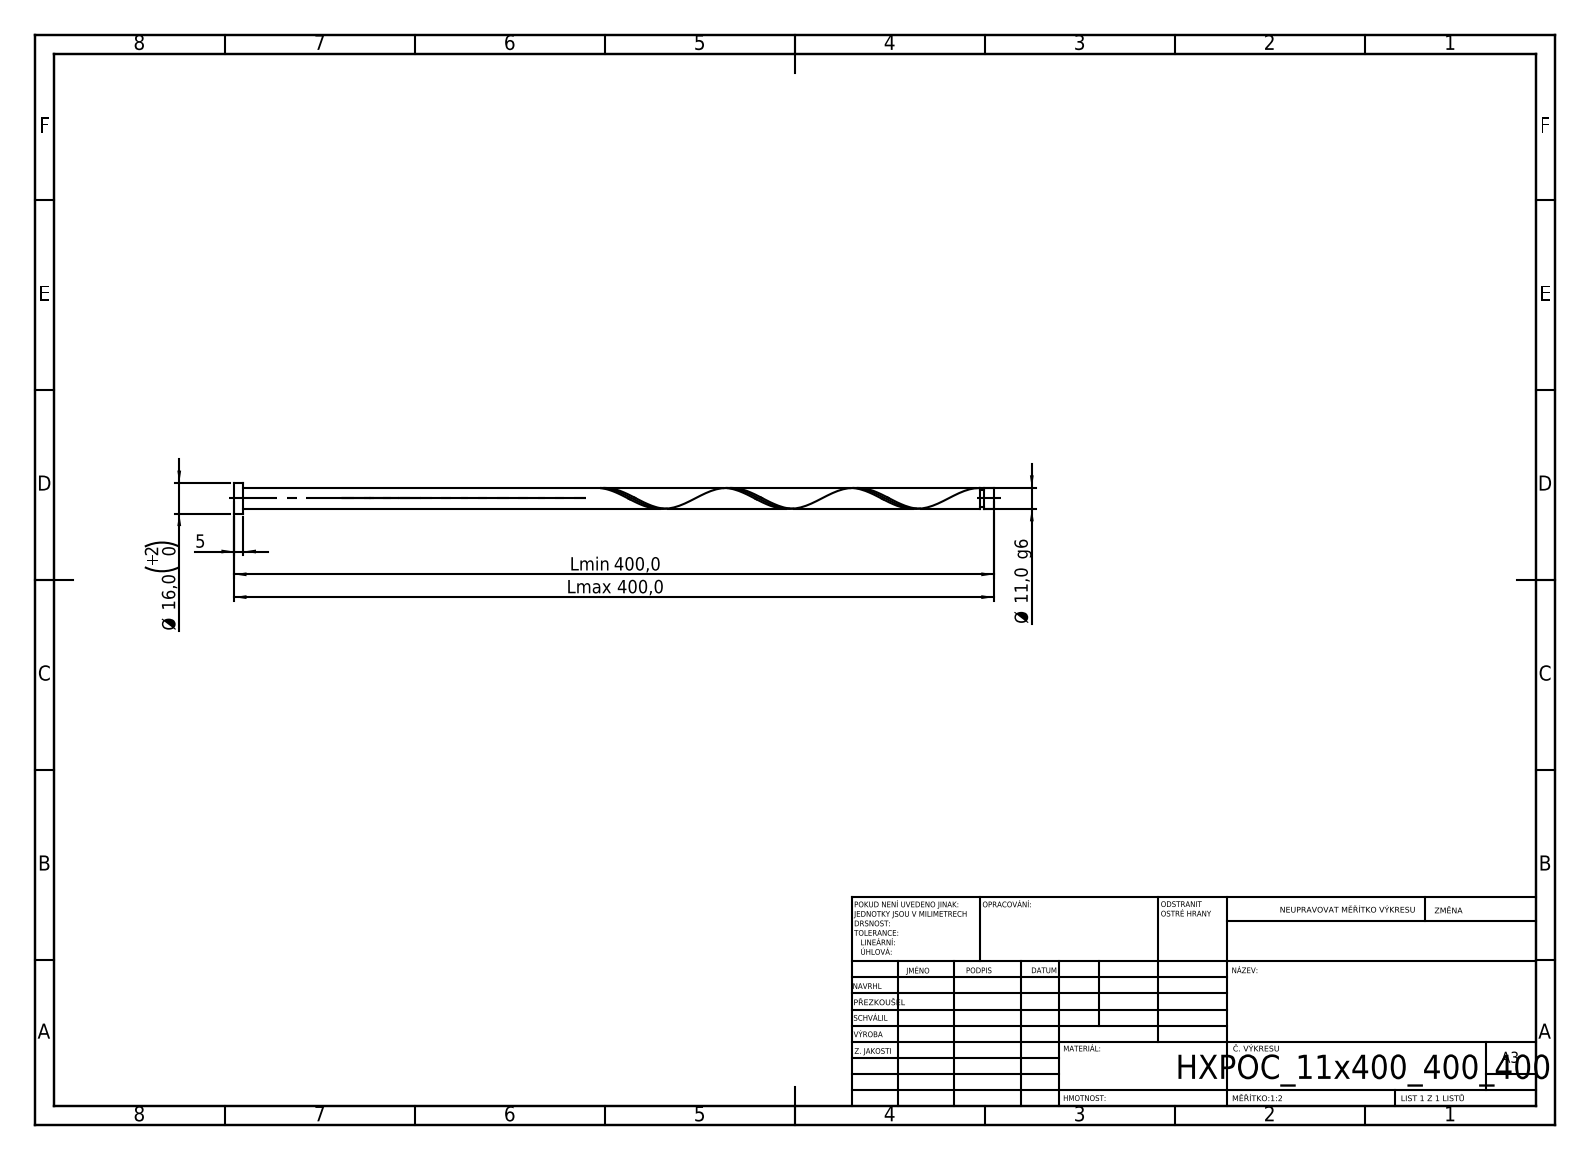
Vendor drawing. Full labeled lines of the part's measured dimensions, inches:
STEP written by: SolidWorks 2019 (CONFIG_CONTROL_DESIGN)
Units: inches
Bodies: 1 solid, 21 faces (6 planar, 14 cylindrical, 1 other)
Overall size (bounding box): 15.748 × 0.63 × 0.63
Volume: 2.325 in³ · Surface area: 22.63 in²
Round bosses / shafts (diameter × count): ⌀0.63 ×1, ⌀0.433 ×1, ⌀0.346 ×1
Main face-to-face distances: 0.197, 15.748, 15.551, 15.553, 15.356, 0.195, 15.467, 15.27, 0.087, 0.281
